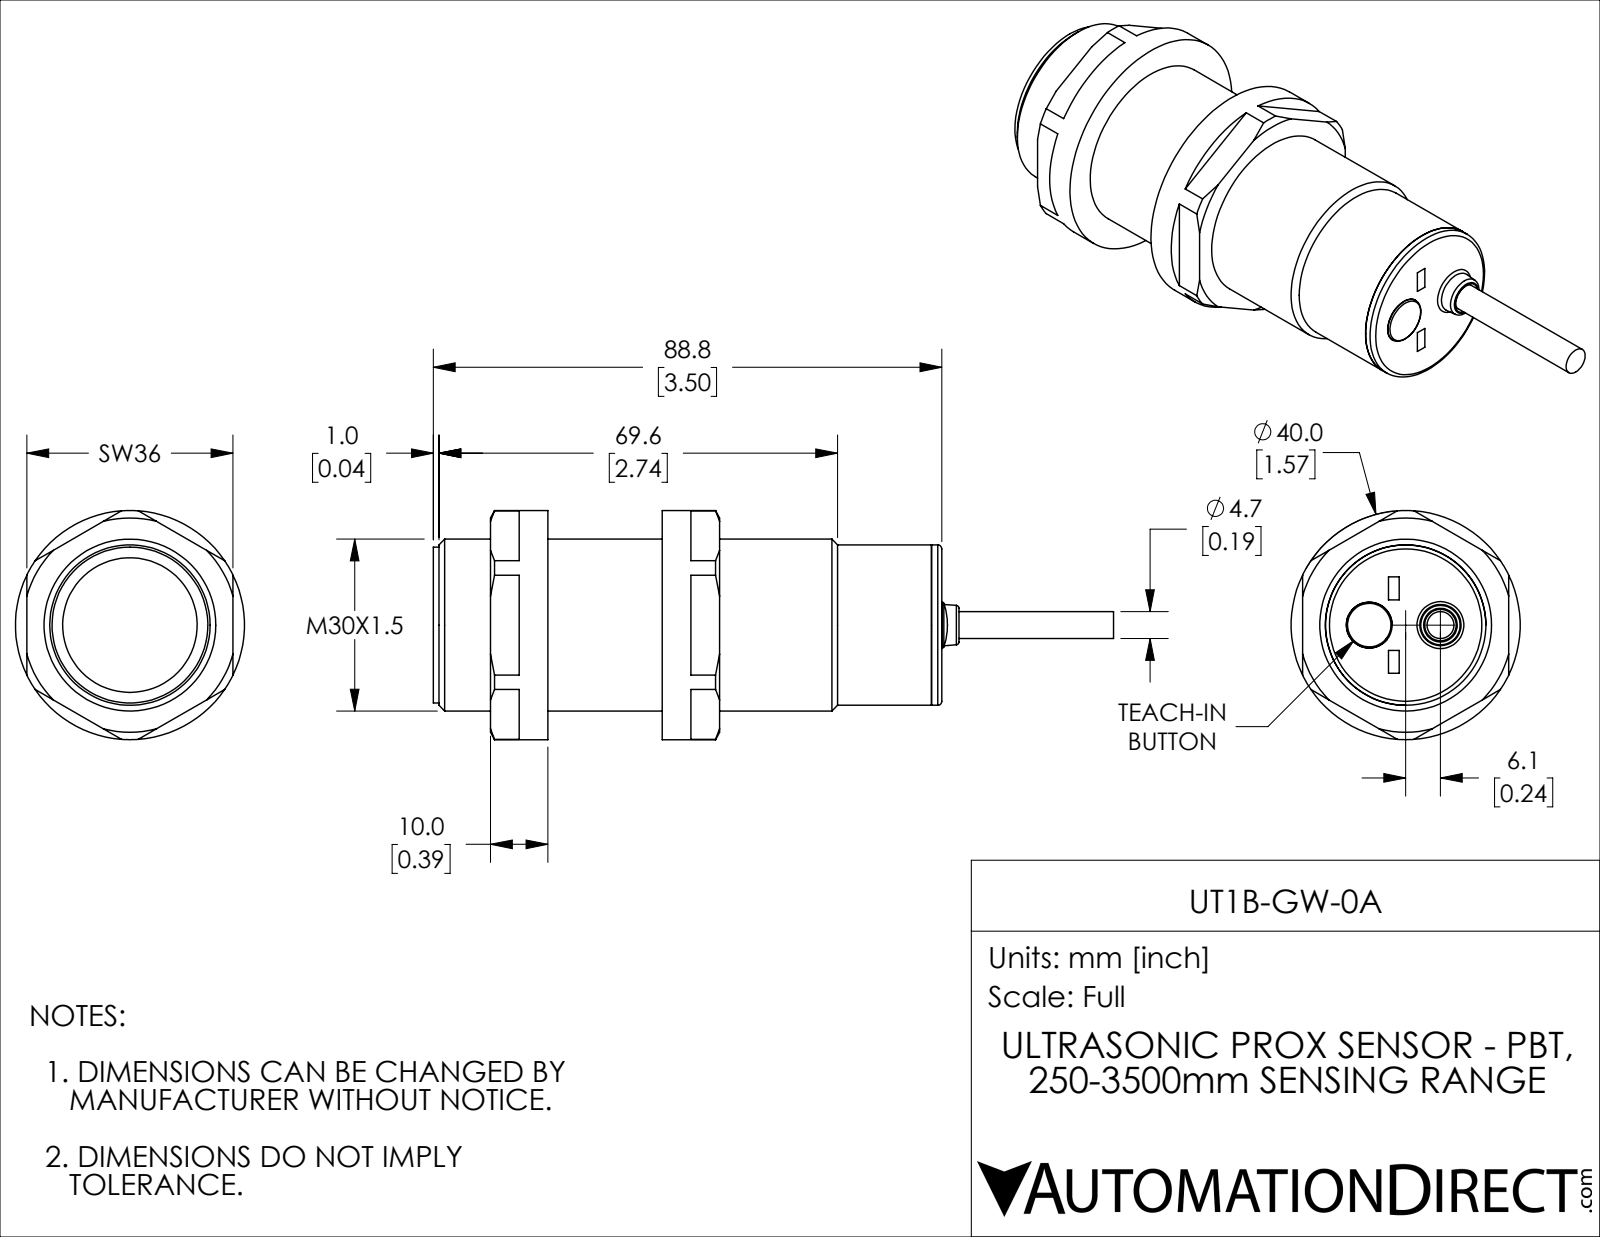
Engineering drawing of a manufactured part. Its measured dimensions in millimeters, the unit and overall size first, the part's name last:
Units: millimetres
Overall size (bounding box): 118.8 × 40 × 40
Round holes (diameter × count): ⌀4.7 ×1, ⌀8 ×1, ⌀23.5 ×1, ⌀30 ×1
Round bosses / shafts (diameter × count): ⌀40 ×1, ⌀28 ×1, ⌀27.2 ×1
Main face-to-face distances: 86, 30, 10, 20, 5, 87.8, 39, 47, 19, 67
Hole centre spacings: 6.07, 6.36, 12.43
Volume: 71 057 mm³ · Surface area: 19 190 mm²
Bodies: 7 solids, 101 faces (43 planar, 26 cylindrical, 32 other)
Part name (STEP PRODUCT): UT1B-GW-0A
STEP written by: SolidWorks 2018 (AUTOMOTIVE_DESIGN)
